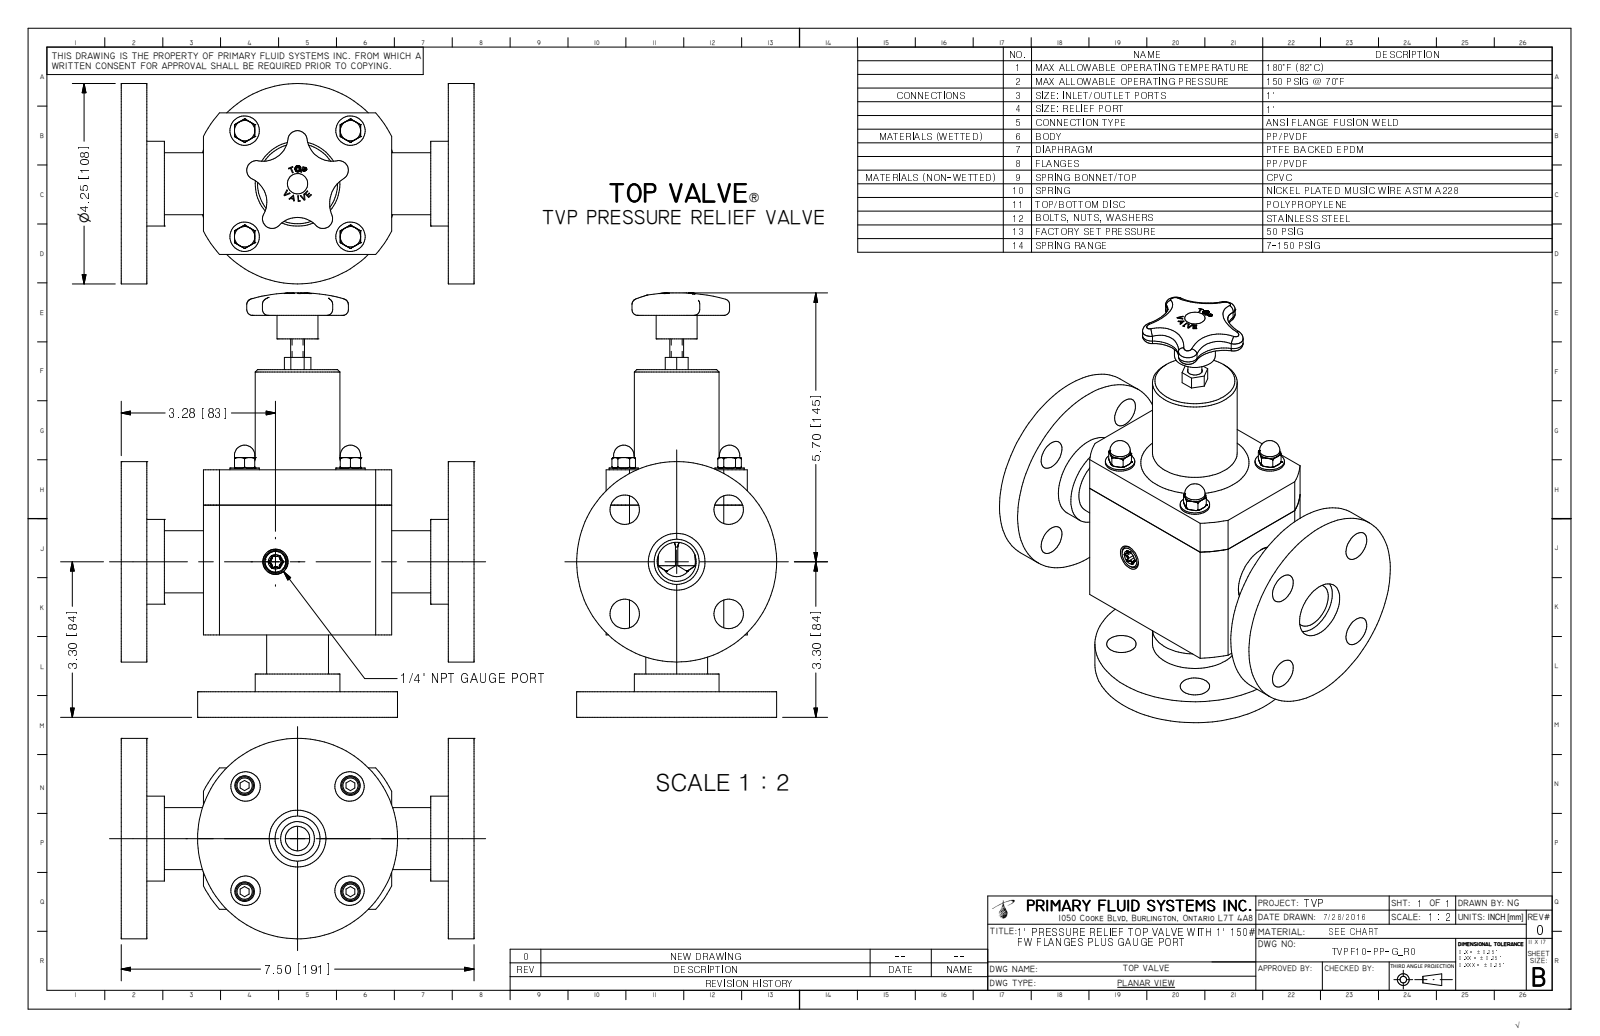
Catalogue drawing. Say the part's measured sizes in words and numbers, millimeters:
The part is named "TVPF10-PP-G_R0". Its 3-D file was written by "Autodesk Inventor 2009 (AUTOMOTIVE_DESIGN)". It is 1 solid with 402 faces: 167 planar, 78 cylindrical and 157 other. Overall it measures 228.6 by 190.5 by 108 millimeters. Its volume is 1 139 000 cubic millimeters and its surface area 157 200 square millimeters. Round holes: 8 of diameter 15.9, 4 of diameter 4.4, 2 of diameter 24.3, 2 of diameter 30.6, 1 of diameter 64.1. Round bosses or shafts: 4 of diameter 15.9, 4 of diameter 11, 4 of diameter 9.5, 2 of diameter 108, 2 of diameter 45.7, 2 of diameter 33.4, 1 of diameter 63.5, 1 of diameter 22.1. Partial cylindrical surfaces (rounded edges, fillets, slot ends): 6 of radius 0.7, 5 of radius 2.2, 5 of radius 5.2, 4 of radius 13.6, 4 of radius 16.7, 1 of radius 15.9, 1 of radius 18.9, 1 of radius 56.8. The main face-to-face distances are 13.8, 176.7, 44.5, 30.6, 190.5, 76.2, 146.1, 132.2, 162.8, 133.4. The hole center spacings are 39.7, 56.1, 56.6, 56.6, 57.2, 79.4, 80.1, 0.7.
